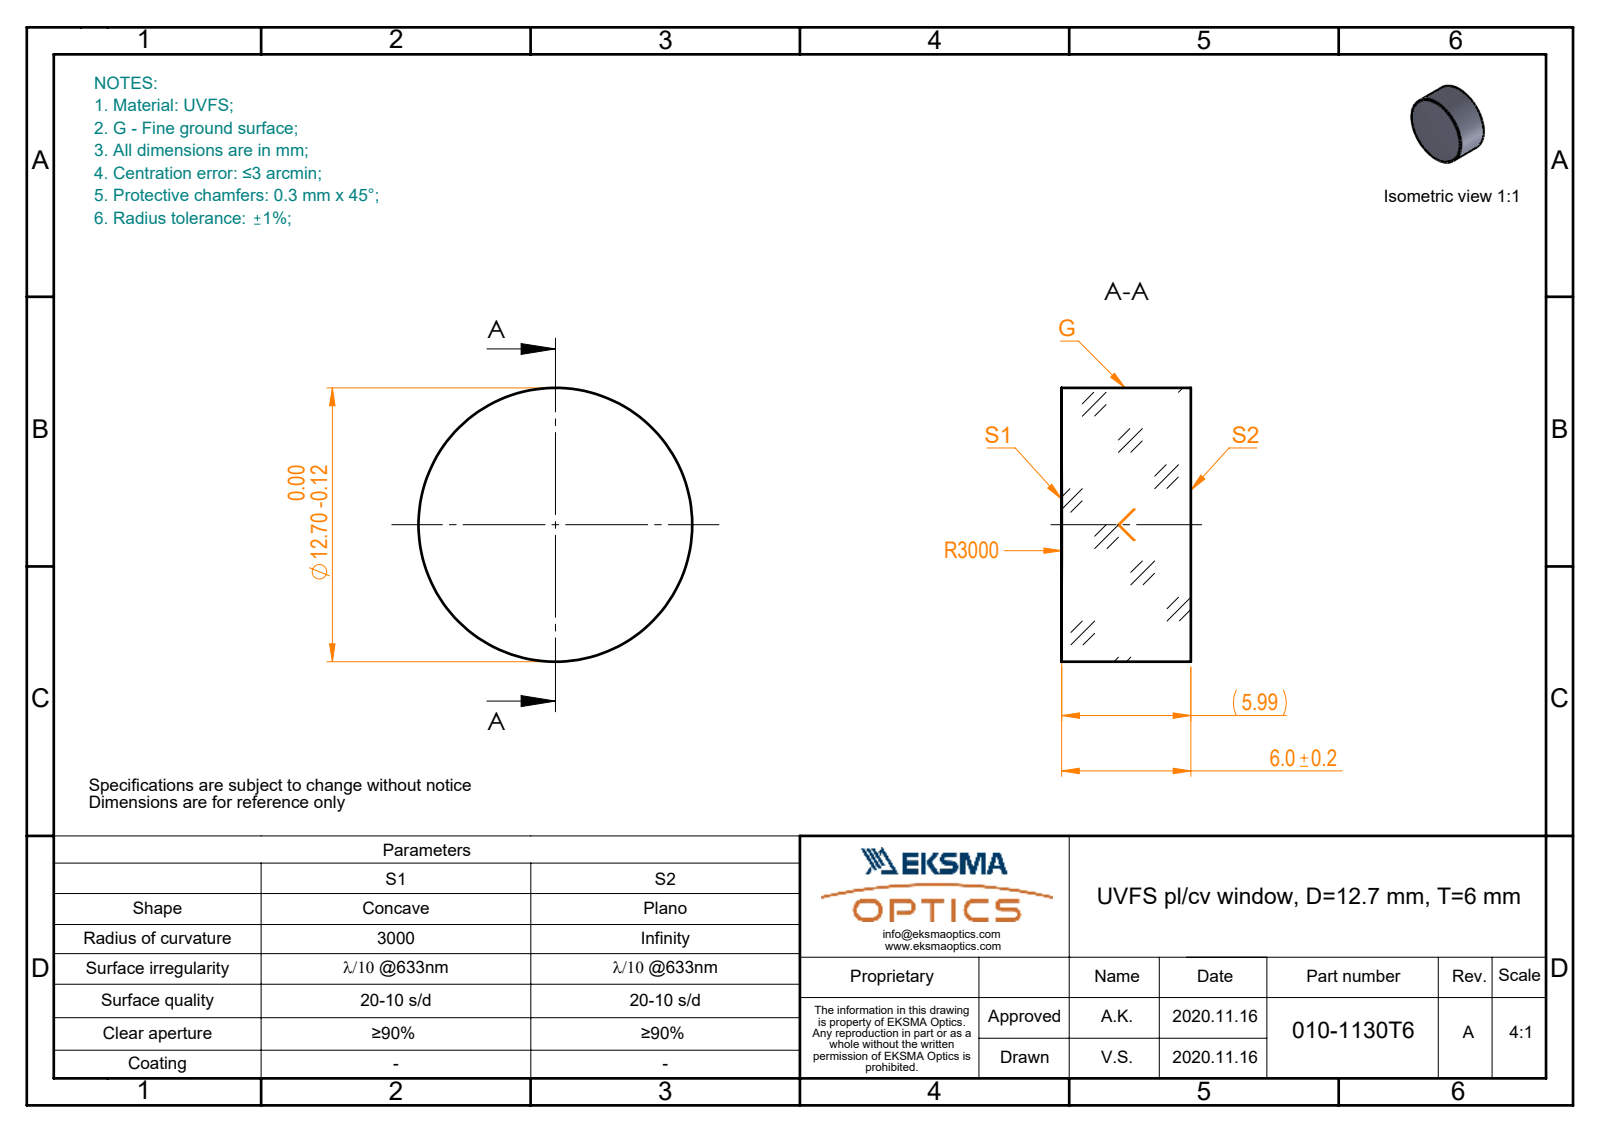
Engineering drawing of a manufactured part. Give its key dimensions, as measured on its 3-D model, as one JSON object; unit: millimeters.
{"part_name": "010-1130T6_UVFS_PCV_window", "step_written_by": "SolidWorks 2019 (CONFIG_CONTROL_DESIGN)", "units": "millimeters", "bodies": {"solids": 1, "faces": 5, "planar": 1, "cylindrical": 2, "other": 2}, "overall_size": [12.7, 12.7, 6], "volume_mm3": 760, "surface_area_mm2": 493, "round_bosses_or_shafts": [[12.7, 1]]}
